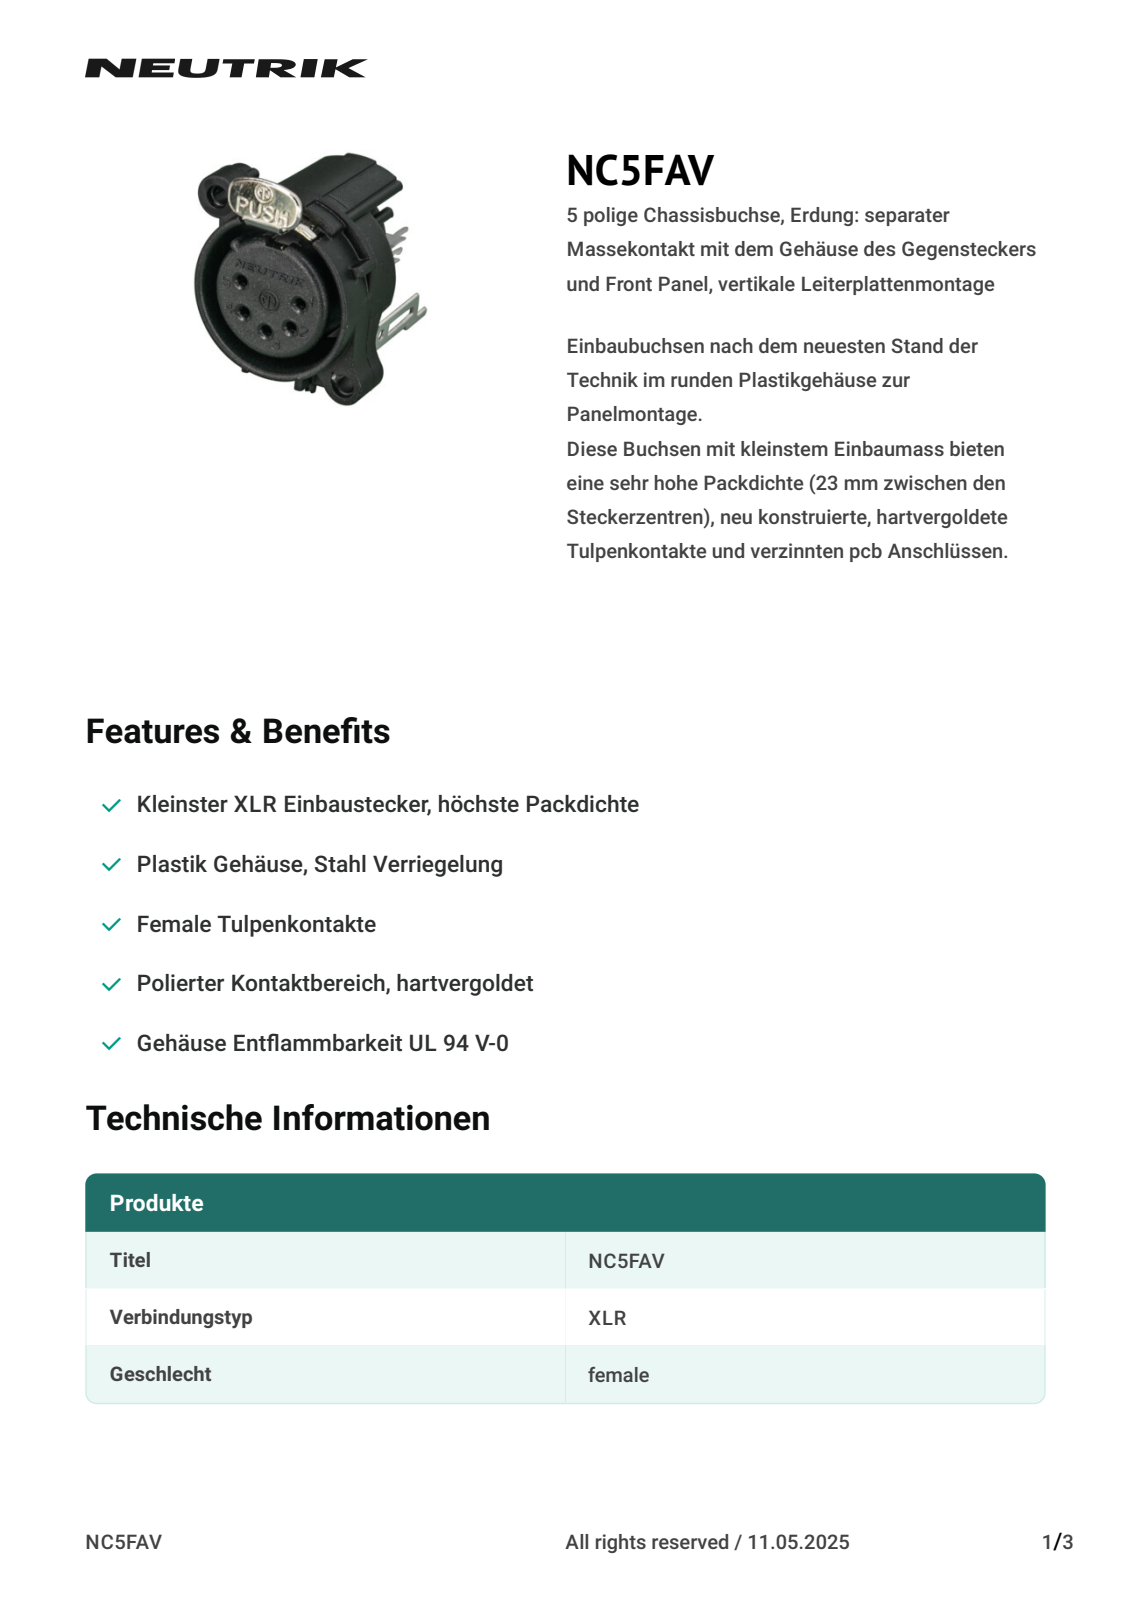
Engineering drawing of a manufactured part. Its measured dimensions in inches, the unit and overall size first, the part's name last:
Units: inches
Overall size (bounding box): 1.342 × 1.206 × 0.996
Round holes (diameter × count): ⌀0.055 ×5, ⌀0.059 ×2, ⌀0.093 ×2, ⌀0.118 ×2, ⌀0.098 ×1, ⌀0.099 ×1
Round bosses / shafts (diameter × count): ⌀0.059 ×5, ⌀0.118 ×1, ⌀0.086 ×1
Partial cylindrical surfaces — rounded edges, fillets, slot ends (radius × count): R0.008 ×261, R0.02 ×28, R0.03 ×13, R0.005 ×9, R0.031 ×8, R0.016 ×6, R0.01 ×4, R0.079 ×4
Main face-to-face distances: 0.059, 0.512, 0.02, 0.634, 0.122, 0.063, 0.571, 0.16, 0.06, 0.22
Hole centre spacings: 0.169, 0.143, 0.168, 0.551, 0.714, 0.143, 0.163, 0.259
Volume: 0.322 in³ · Surface area: 9.303 in²
Bodies: 1 solid, 2142 faces (1111 planar, 465 cylindrical, 566 other)
Part name (STEP PRODUCT): NC5FAV
STEP written by: CREO PARAMETRIC BY PTC INC, 2019080 (CONFIG_CONTROL_DESIGN)
